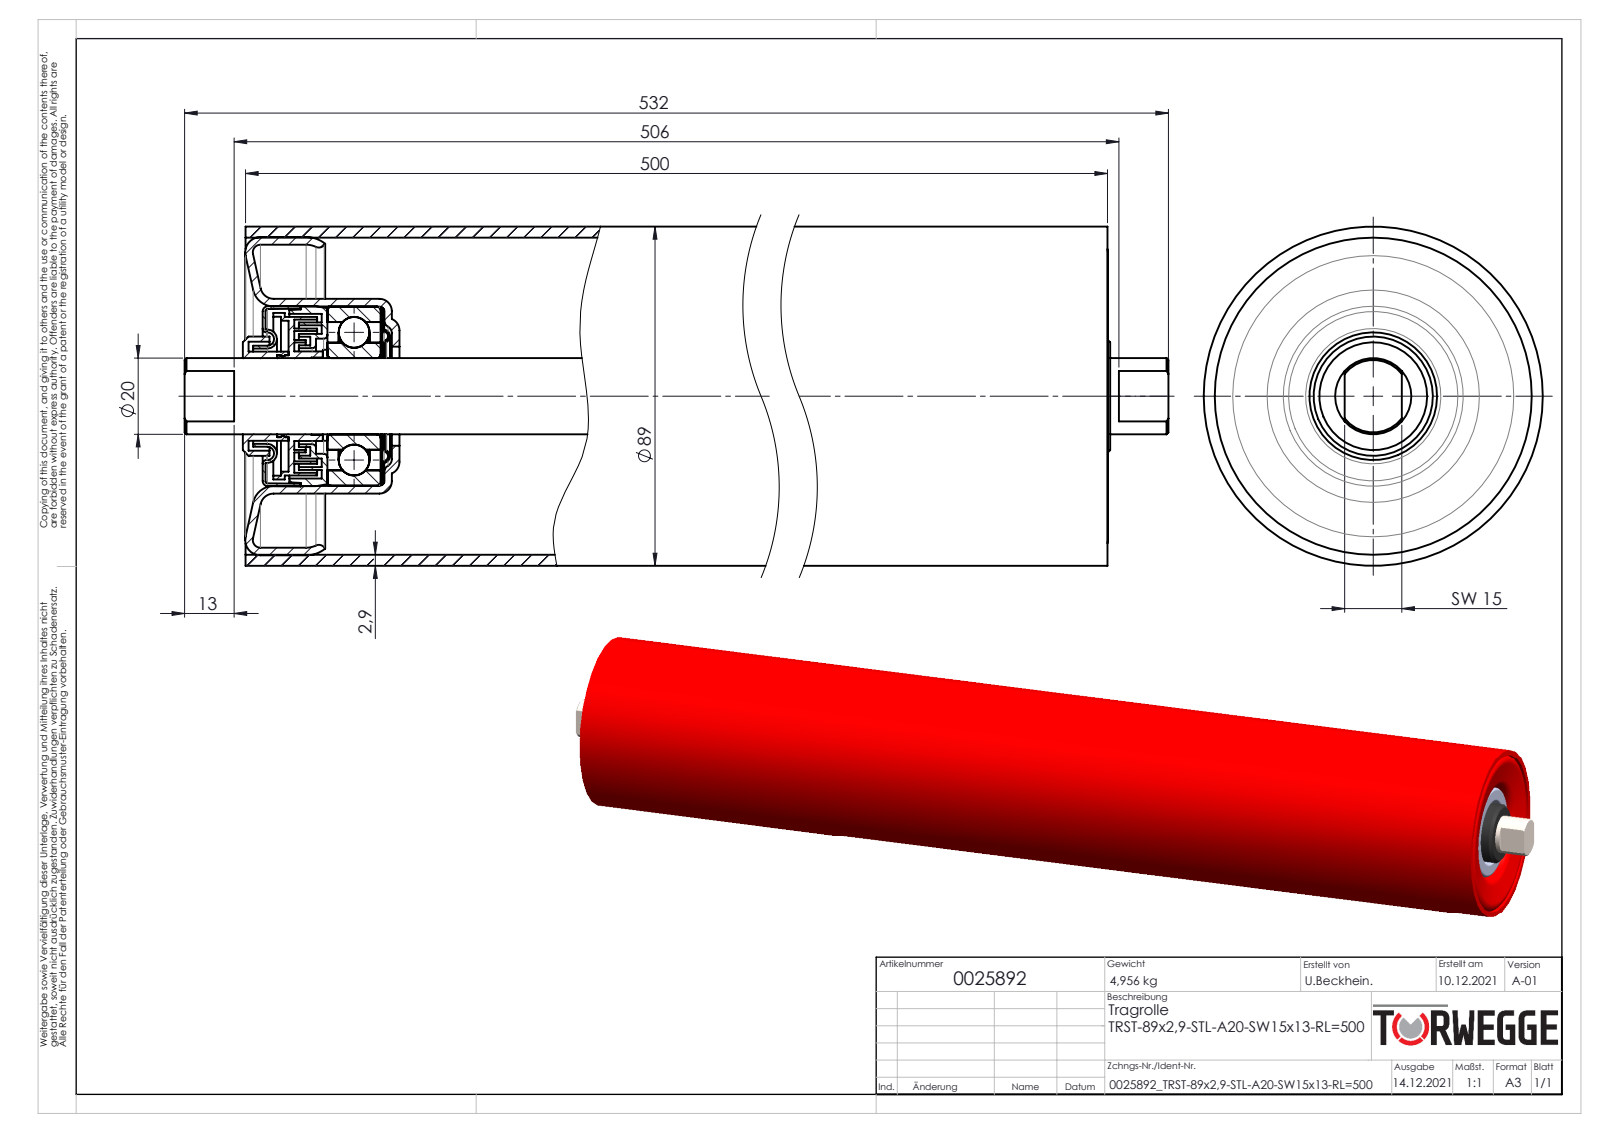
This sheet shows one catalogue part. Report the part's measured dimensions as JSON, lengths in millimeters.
{"part_name": "0025892", "step_written_by": "SolidWorks 2020 (AUTOMOTIVE_DESIGN)", "units": "millimeters", "bodies": {"solids": 24, "faces": 606, "planar": 114, "cylindrical": 244, "other": 248}, "overall_size": [532, 89, 89], "volume_mm3": 710909, "surface_area_mm2": 460844, "round_holes": [[2, 4], [19, 1], [19.6, 1], [20, 1], [20.3, 1], [21, 1], [21.5, 1], [25, 1], [25.2, 1], [26, 1], [28.2, 1], [28.6, 1]], "round_bosses_or_shafts": [[23.9, 2], [89, 1], [83.5, 1], [51.1, 1], [47.2, 1], [47, 1], [46.5, 1], [43.7, 1]], "partial_cylinders_radius": [[2, 8], [13.5, 1]], "face_to_face_distances": [14, 443.02, 14.92, 442.1, 0.92, 428.1, 457.02, 10.2, 24.2, 25.12], "hole_center_spacings": [11.49, 11.5, 22.55, 3.99, 4, 21.43, 22.99]}
